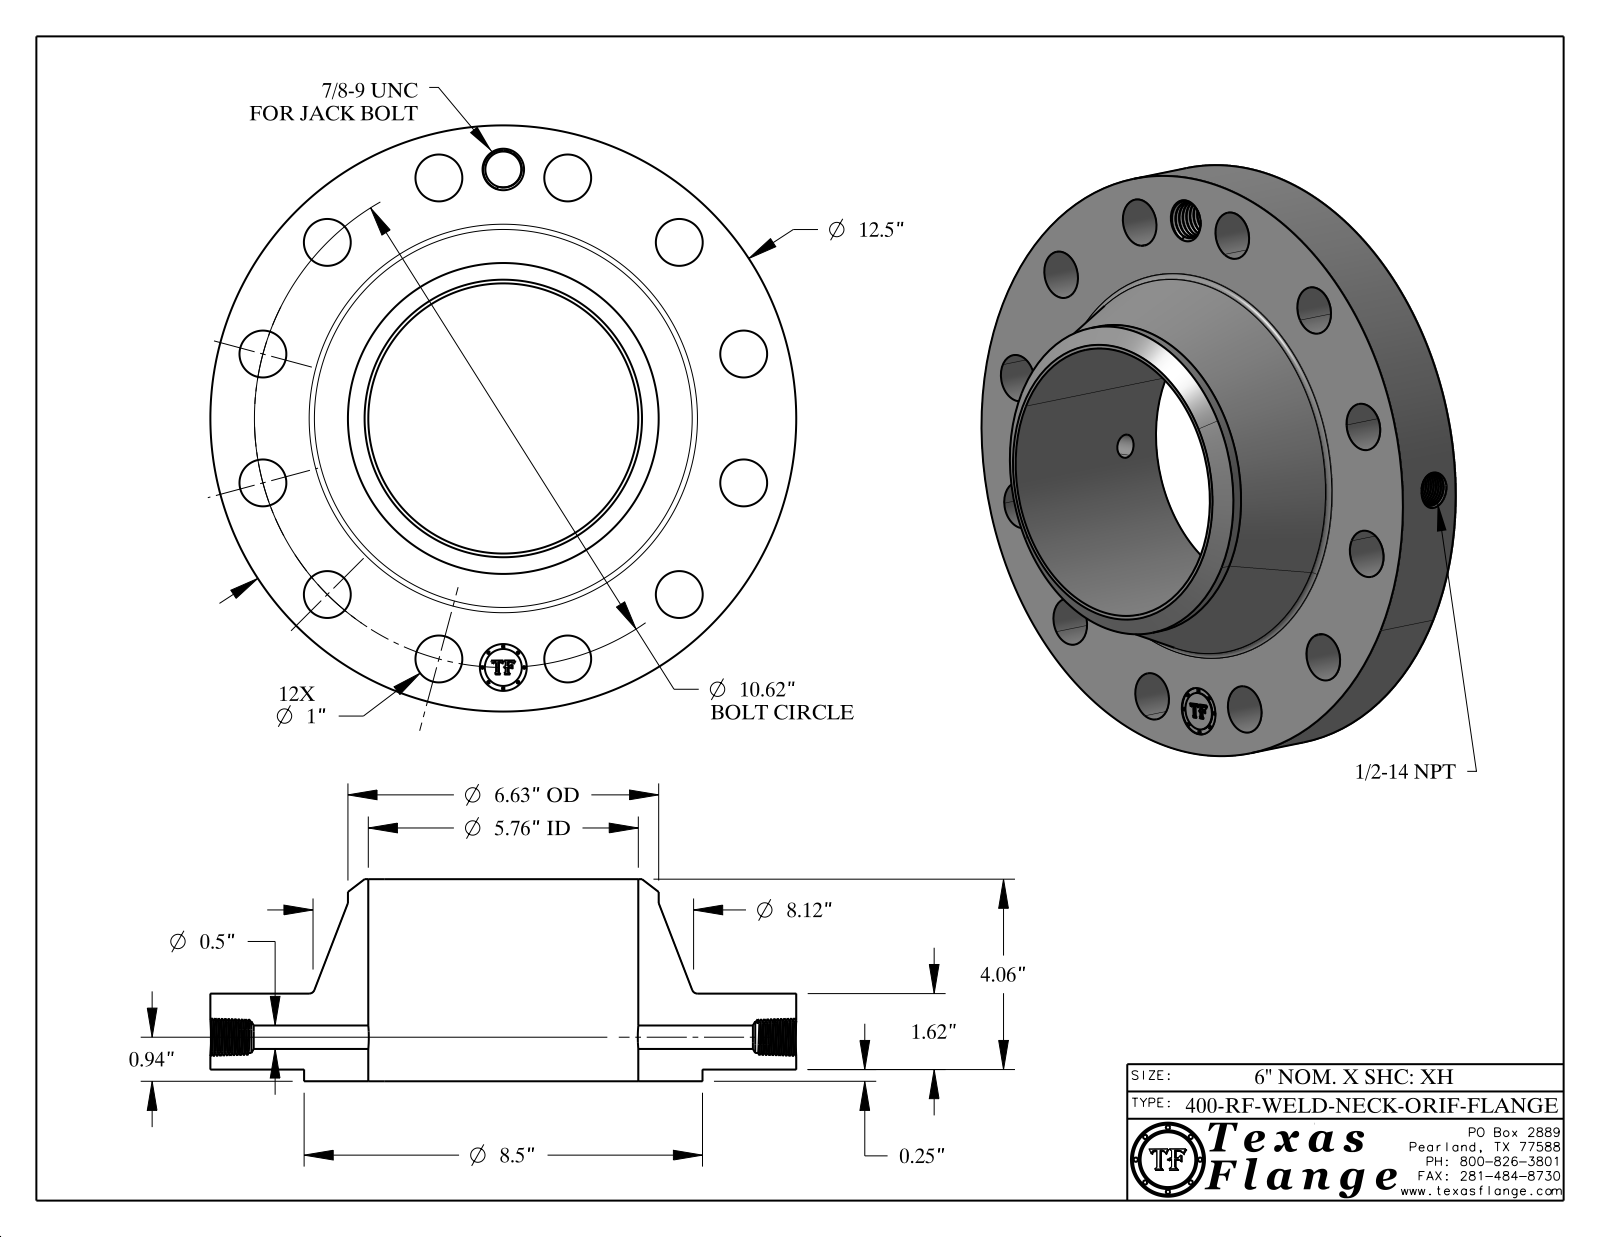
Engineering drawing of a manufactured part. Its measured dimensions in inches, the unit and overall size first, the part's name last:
Units: inches
Overall size (bounding box): 12.5 × 12.5 × 4.31
Round holes (diameter × count): ⌀1 ×13, ⌀0.5 ×1, ⌀0.672 ×1, ⌀0.766 ×1, ⌀5.761 ×1
Round bosses / shafts (diameter × count): ⌀0.061 ×8, ⌀12.5 ×1, ⌀8.5 ×1, ⌀6.63 ×1, ⌀0.788 ×1
Main face-to-face distances: 1.62, 0.25, 1.87, 4.31, 4.06, 2.44, 0.015, 1.855, 1.605, 2.455
Hole centre spacings: 5.31, 7.509, 9.197, 10.258, 5.31, 2.748, 10.62, 1.386
Volume: 182.2 in³ · Surface area: 439.6 in²
Bodies: 1 solid, 773 faces (369 planar, 100 cylindrical, 304 other)
Part name (STEP PRODUCT): 400-RF-WELD-NECK
STEP written by: CATIA V5 STEP AP214 (AUTOMOTIVE_DESIGN)
